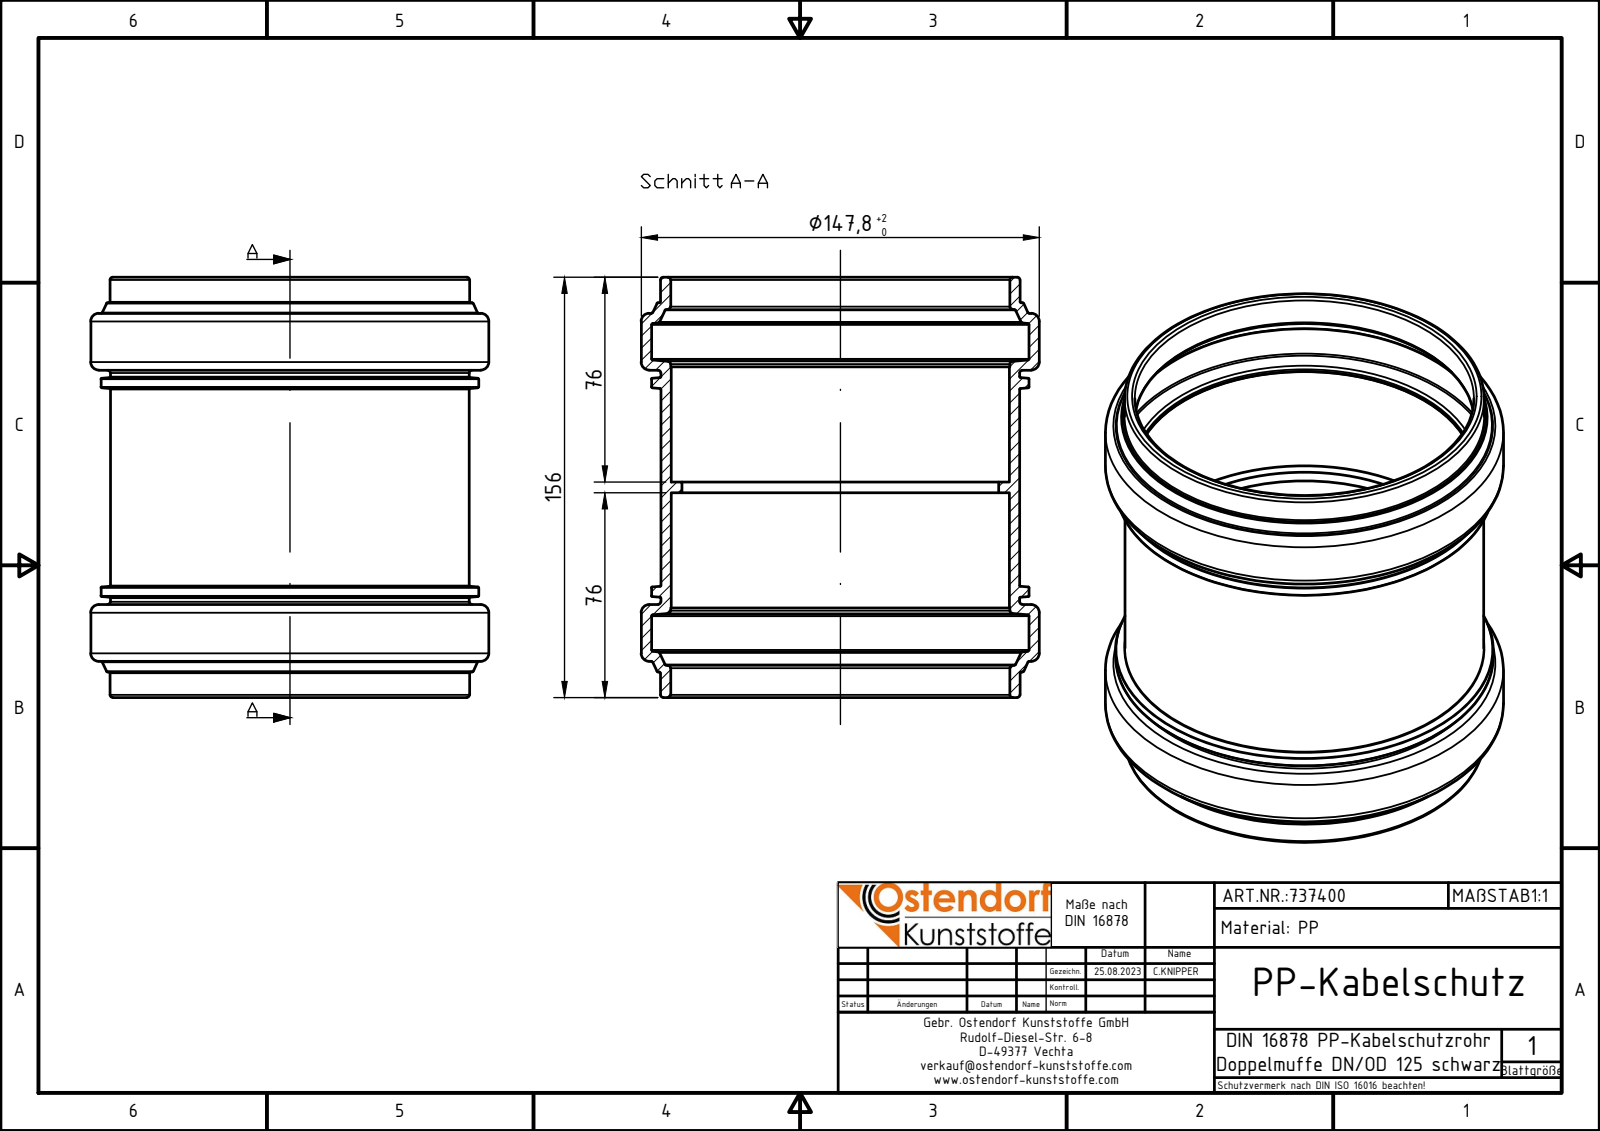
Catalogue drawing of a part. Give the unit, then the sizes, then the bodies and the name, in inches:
Units: inches
Overall size (bounding box): 6.142 × 5.819 × 5.819
Round holes (diameter × count): ⌀4.63 ×1, ⌀4.945 ×1, ⌀4.957 ×1, ⌀5.52 ×1
Round bosses / shafts (diameter × count): ⌀5.819 ×1, ⌀5.256 ×1, ⌀5.244 ×1
Main face-to-face distances: 1.634, 1.791, 0.157, 1.358, 2.992, 3.15, 4.783, 3.425, 6.142, 0.528
Volume: 18.23 in³ · Surface area: 245.4 in²
Bodies: 1 solid, 80 faces (12 planar, 18 cylindrical, 50 other)
Part name (STEP PRODUCT): 737400z
STEP written by: Autodesk Inventor 2024 (AUTOMOTIVE_DESIGN)
